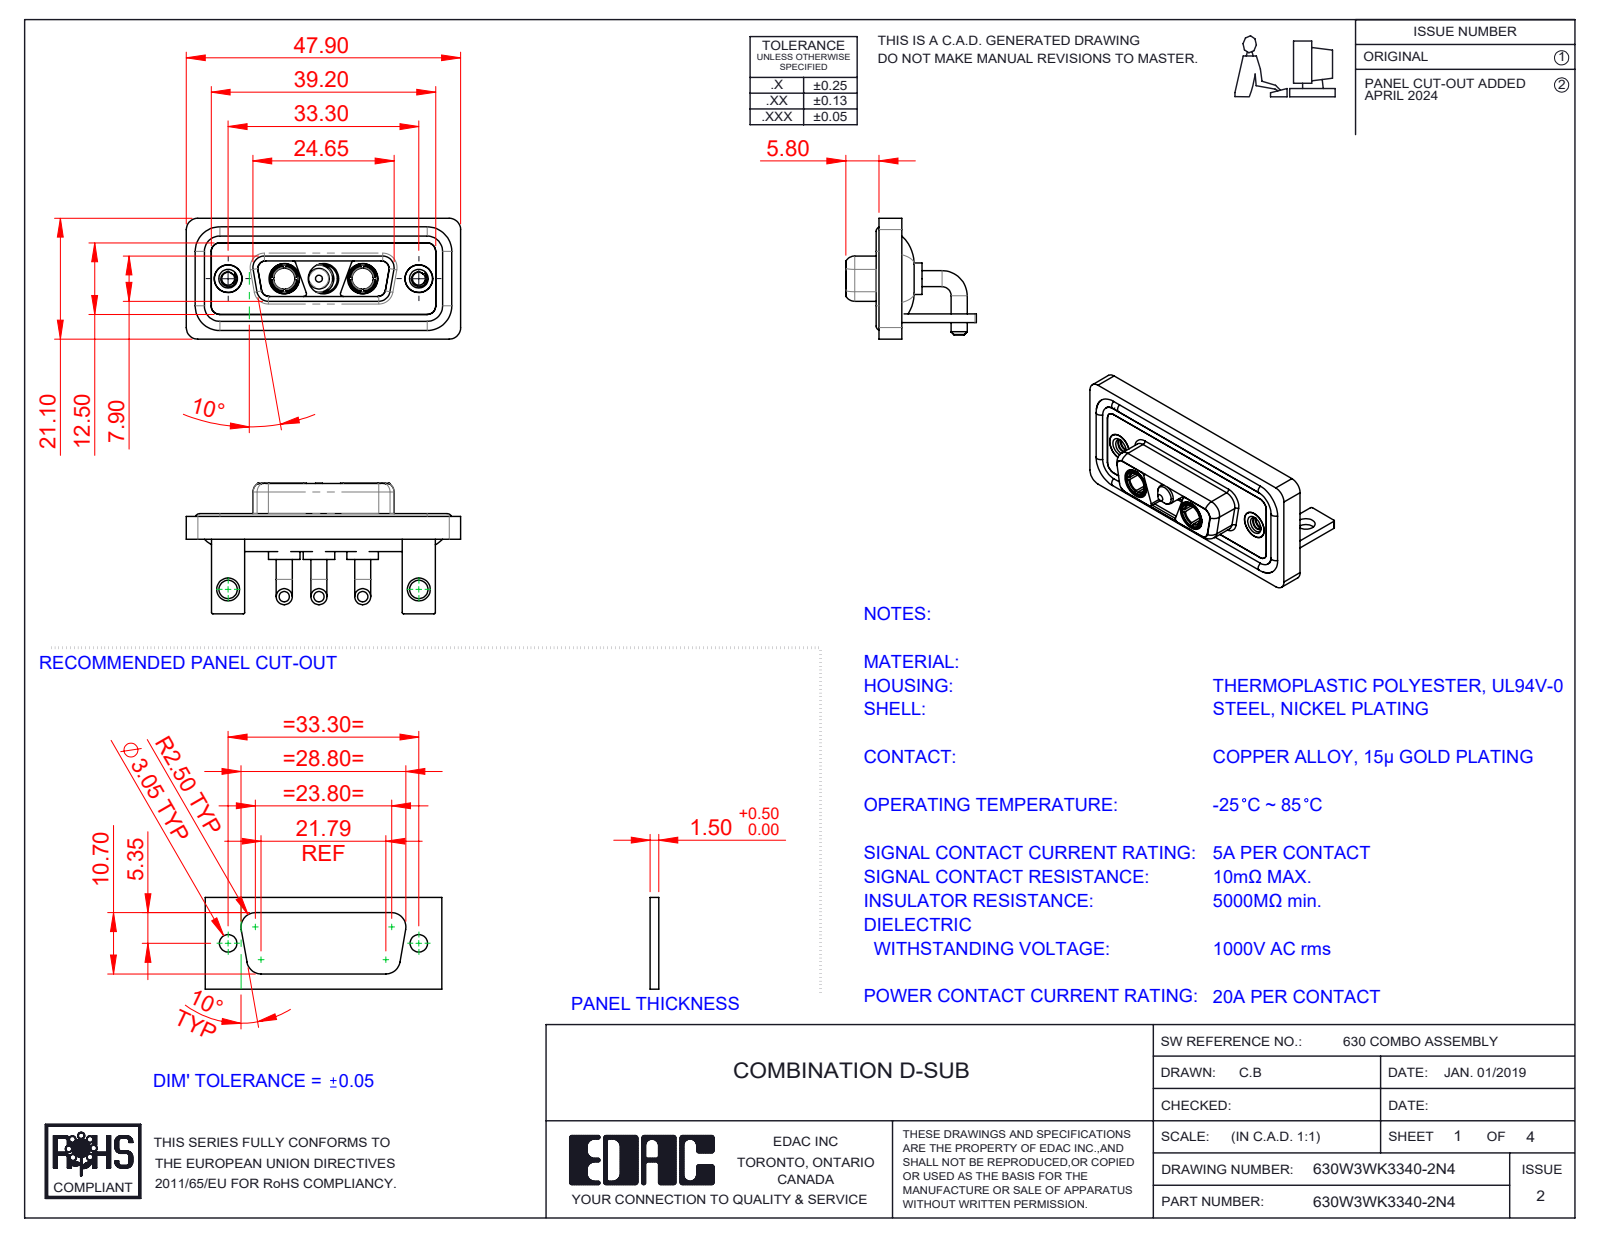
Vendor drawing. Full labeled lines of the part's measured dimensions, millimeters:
Part name (STEP PRODUCT): 630Combo Waterproof Housing_15 Contacts; 630Combo Shell Front_15 Contacts; 630Combo Housing_3WK3; 630Combo Stabilizer Bracket_50 Contacts (+5 more)
STEP written by: SolidWorks 2023 (CONFIG_CONTROL_DESIGN)
Units: millimetres
Bodies: 15 solids, 643 faces (198 planar, 288 cylindrical, 157 other)
Overall size (bounding box): 47.9 × 22.8 × 21.1
Volume: 6 398 mm³ · Surface area: 10 474 mm²
Round holes (diameter × count): ⌀4.85 ×5, ⌀5.3 ×3, ⌀2.26 ×2, ⌀3.2 ×2, ⌀3.7 ×2, ⌀4 ×2, ⌀4.05 ×2, ⌀5 ×2
Round bosses / shafts (diameter × count): ⌀2.8 ×6, ⌀1.6 ×4, ⌀5.5 ×3, ⌀5.2 ×3, ⌀4.75 ×3, ⌀3.75 ×3, ⌀4.96 ×2, ⌀4.95 ×2
Partial cylindrical surfaces — rounded edges, fillets, slot ends (radius × count): R2 ×21, R1.5 ×18, R0.25 ×16, R1.35 ×12, R0.5 ×9, R1.6 ×8, R0.6 ×4, R0.65 ×4
Main face-to-face distances: 0.4, 2.9, 1.5, 3.7, 1.8, 1.1, 4.1, 1.6, 2.5, 1.4
Hole centre spacings: 6.85, 9.8, 16.65, 23.5, 33.3, 13.7
